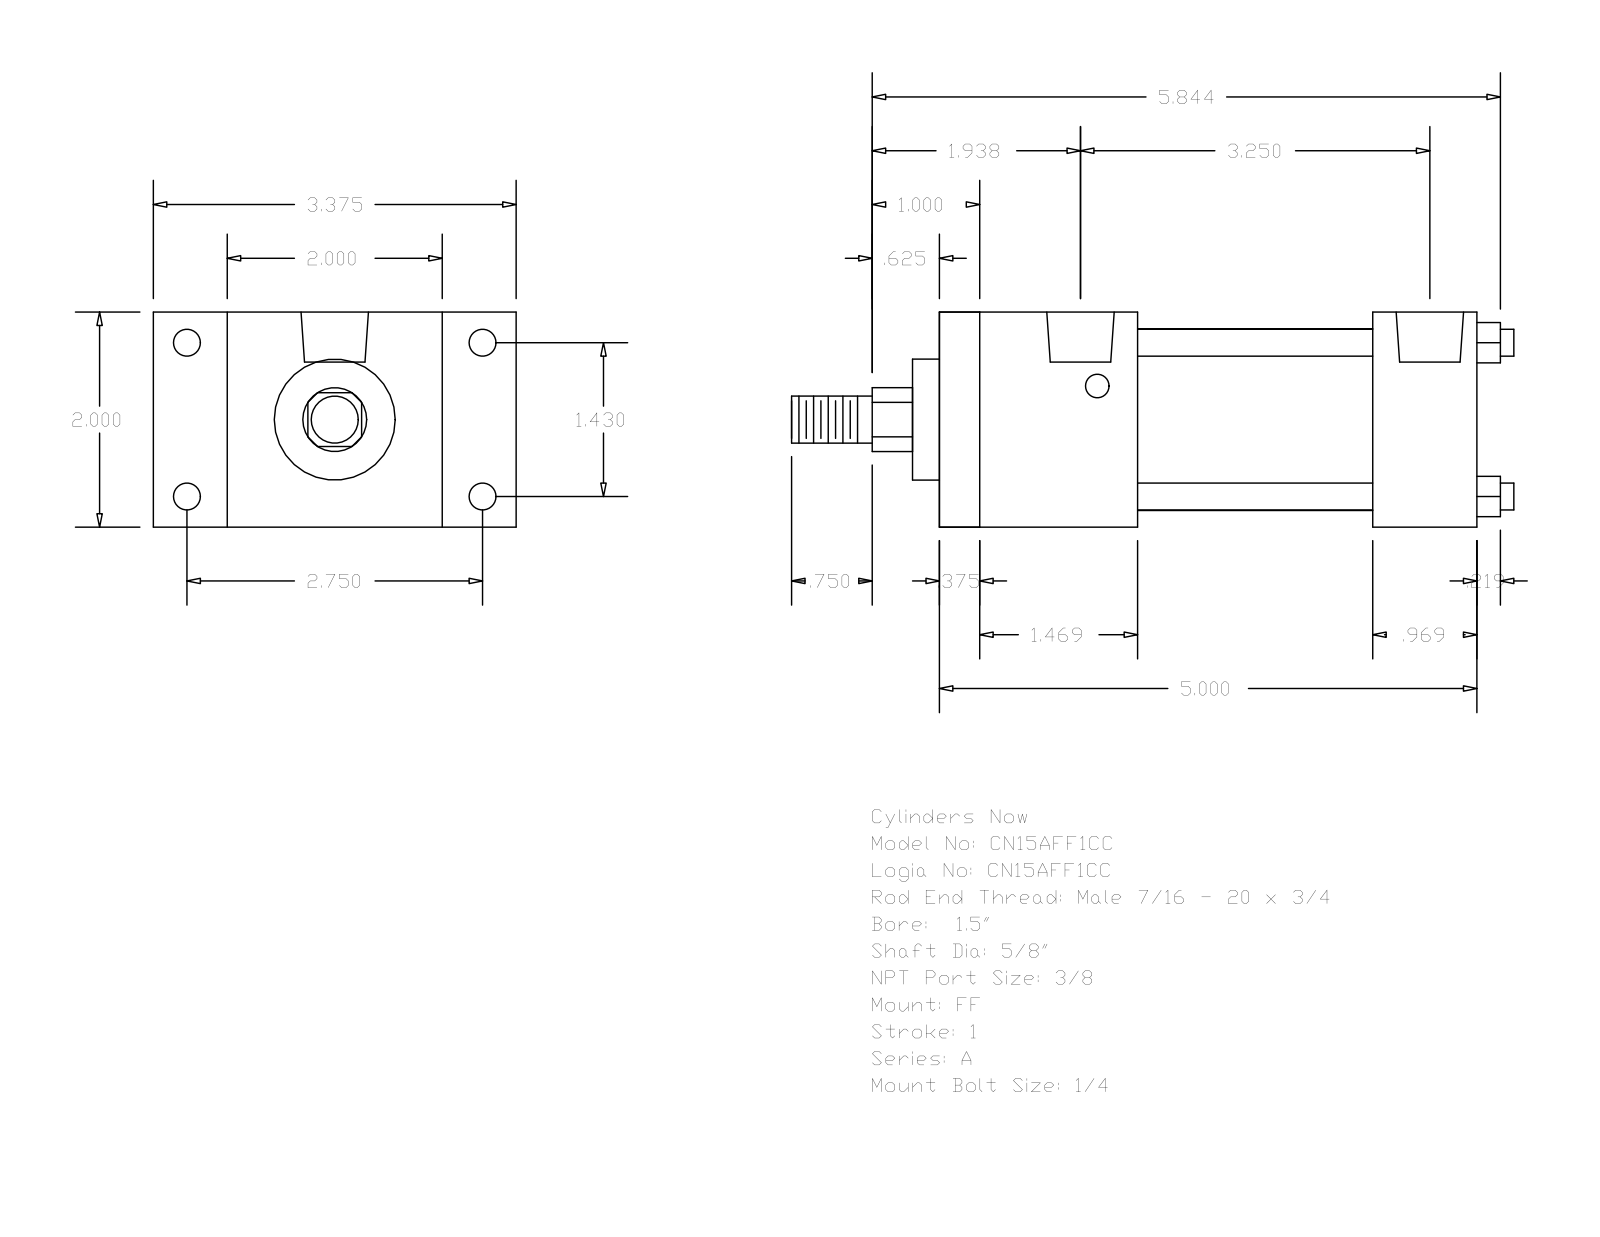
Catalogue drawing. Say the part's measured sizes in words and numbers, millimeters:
The part is named "A_FF__0150_0.625". Its 3-D file was written by "GSSL Pune (CONFIG_CONTROL_DESIGN)". It is 0 solids with 92 faces: 64 planar, 28 cylindrical and 0 other. Overall it measures 170.66 by 85.72 by 50.8 millimeters. Round holes: 4 of diameter 5.56, 4 of diameter 6.35, 2 of diameter 15.93. Round bosses or shafts: 4 of diameter 6.35, 1 of diameter 42.93, 1 of diameter 28.57, 1 of diameter 15.88, 1 of diameter 11.11. Partial cylindrical surfaces (rounded edges, fillets, slot ends): 1 of radius 7.54. The main face-to-face distances are 50.8, 127, 9.52, 117.48, 46.83, 102.39, 37.31, 92.87, 55.56, 80.17. The hole center spacings are 3.97, 36.32, 69.84, 74.61, 78.58, 78.72, 82.55.
